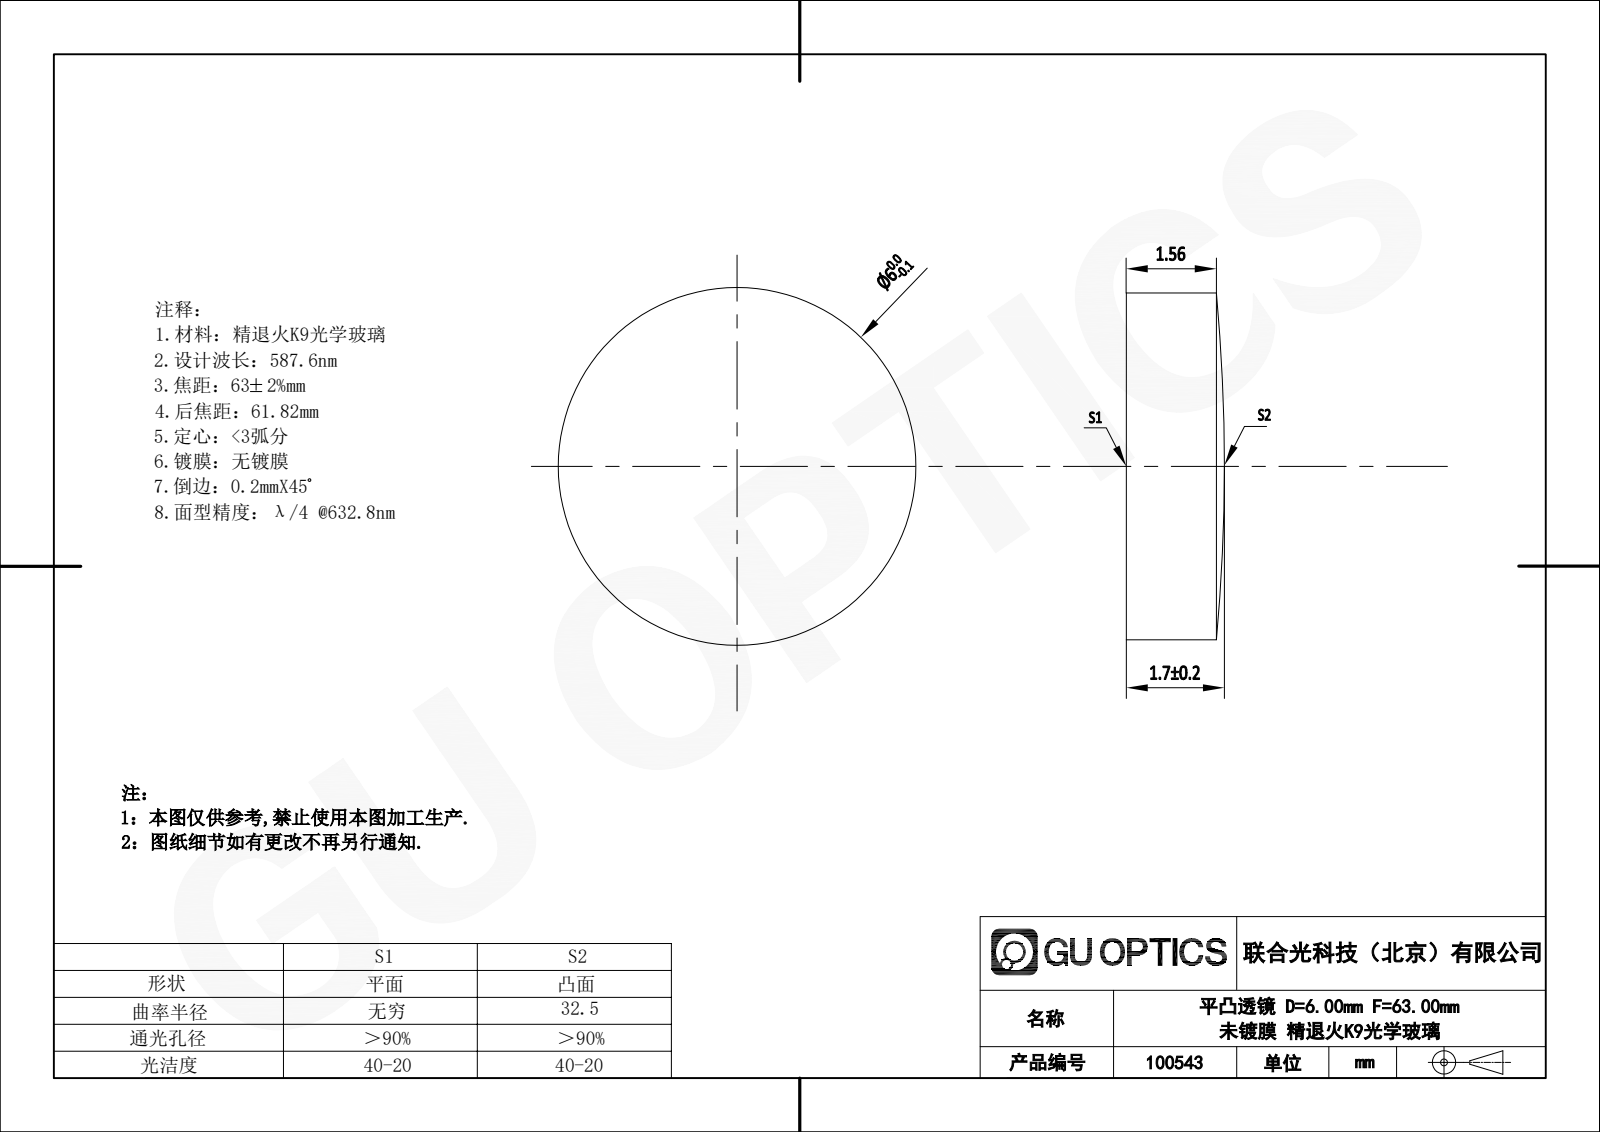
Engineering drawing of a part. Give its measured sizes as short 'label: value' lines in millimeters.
name: 100543
written by: SolidWorks 2020 (CONFIG_CONTROL_DESIGN)
unit: mm
bodies: 1 solid, 5 faces (1 planar, 2 cylindrical, 2 other)
size: 6 × 6 × 1.7
volume: 46 mm³; area: 86 mm²
bosses: 1× ⌀6
